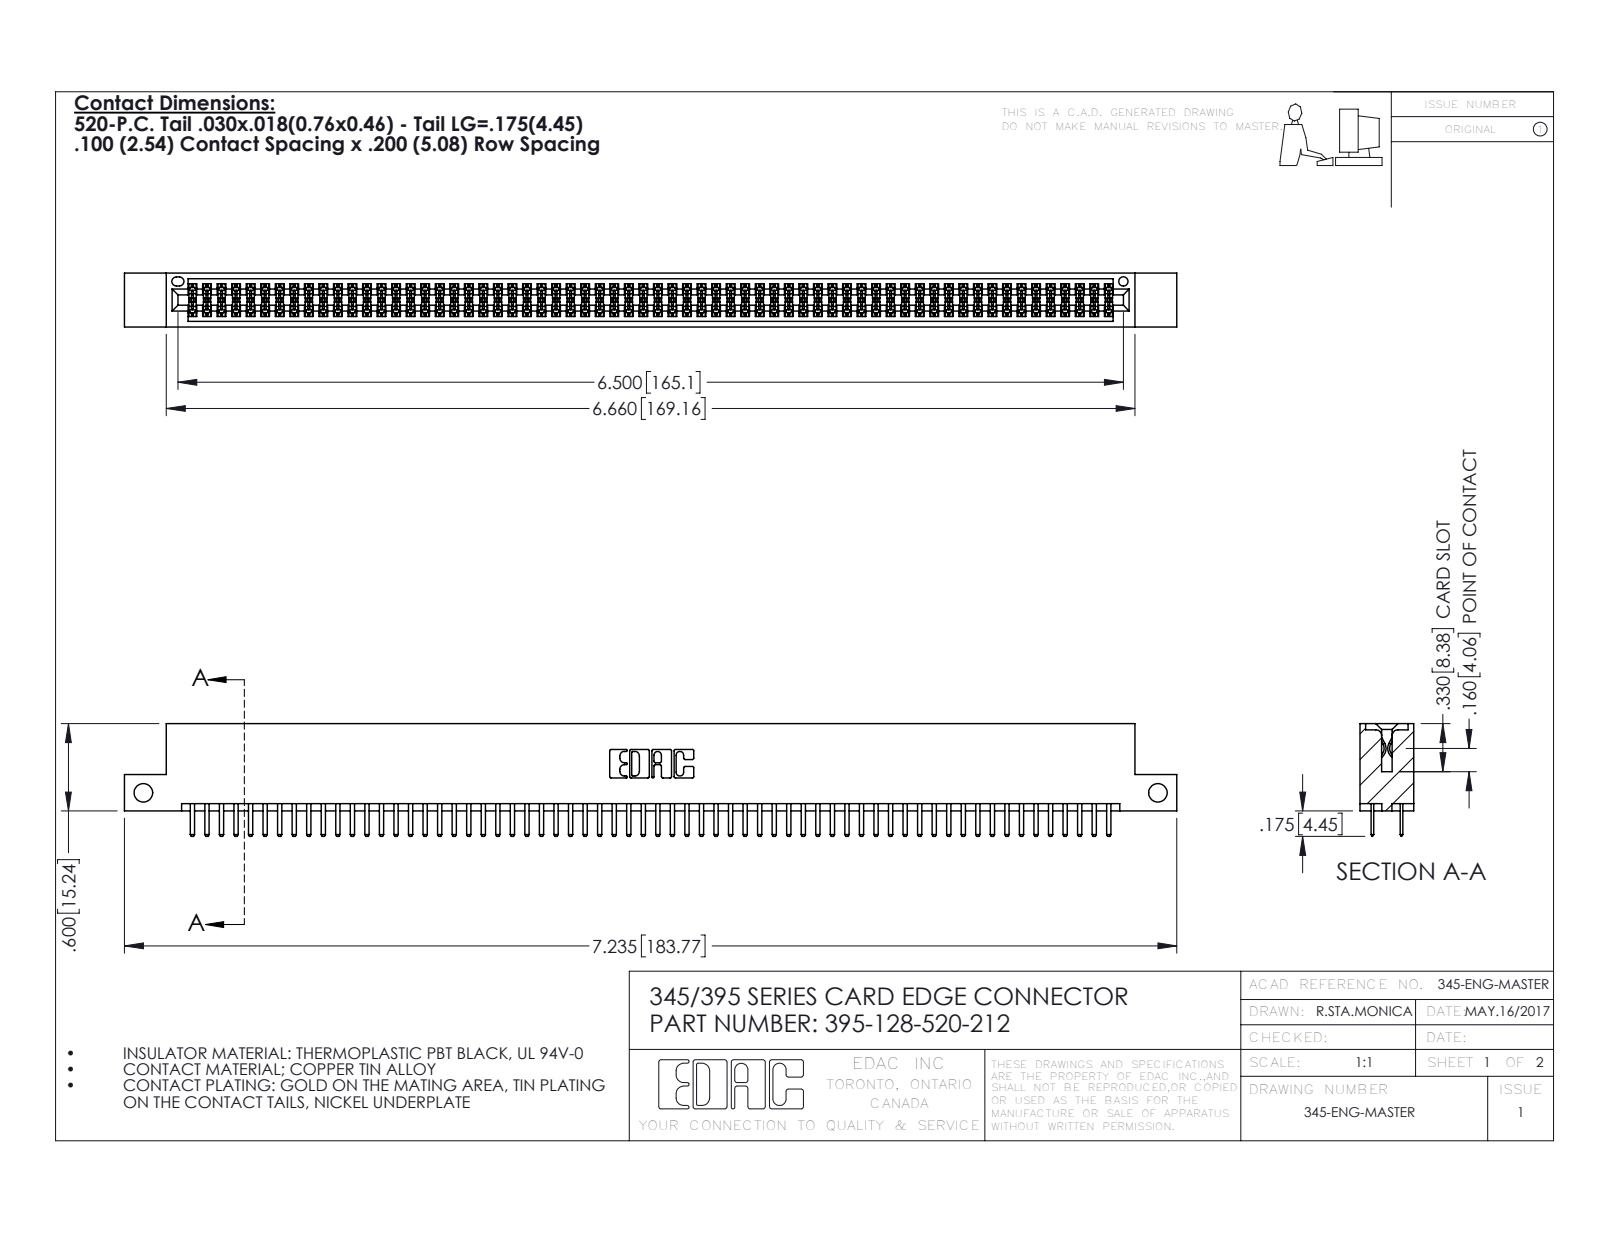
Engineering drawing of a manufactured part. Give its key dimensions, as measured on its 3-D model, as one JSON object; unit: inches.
{"part_name": "395-128-520-212; 345 Part_Flush Mounting Lugs - Side Mount; 345-292-001_345-293-120", "step_written_by": "SolidWorks 2016 (CONFIG_CONTROL_DESIGN)", "units": "inches", "bodies": {"solids": 129, "faces": 7038, "planar": 4560, "cylindrical": 2478, "other": 0}, "overall_size": [7.235, 0.775, 0.37], "volume_in3": 1.093, "surface_area_in2": 41.3, "round_holes": [[0.128, 2], [0.064, 1]], "partial_cylinders_radius": [[0.006, 192], [0.01, 132], [0.01, 22], [0.007, 6], [0.031, 6], [0.026, 3], [0.014, 2], [0.019, 2]], "face_to_face_distances": [0.298, 0.072, 0.2, 0.37, 0.098, 0.272, 0.025, 0.225, 0.022, 0.072], "hole_center_spacings": [6.975]}
